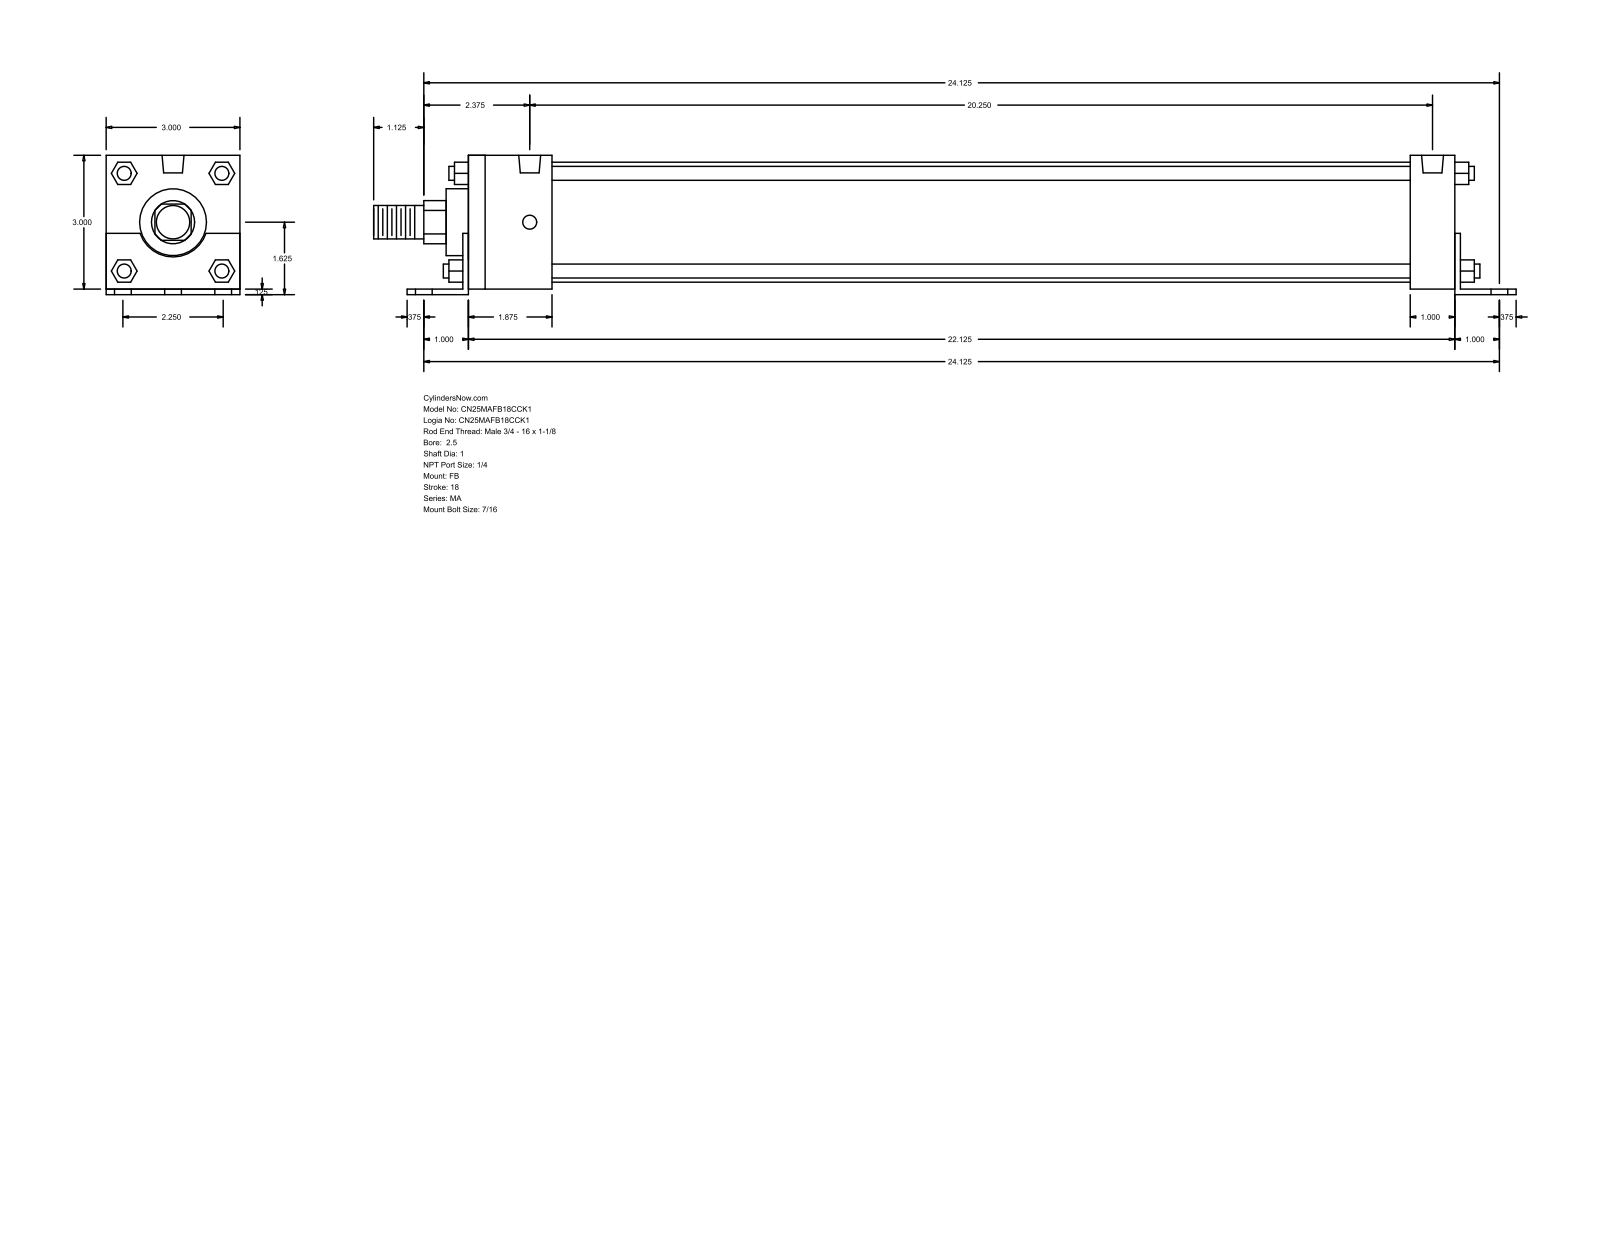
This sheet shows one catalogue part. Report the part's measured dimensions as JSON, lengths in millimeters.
{"part_name": "MA_FB__0250_1", "step_written_by": "GSSL Pune (CONFIG_CONTROL_DESIGN)", "units": "millimeters", "bodies": {"solids": 0, "faces": 140, "planar": 105, "cylindrical": 35, "other": 0}, "overall_size": [650.88, 79.38, 76.2], "round_holes": [[11.11, 6], [7.94, 4], [12.49, 2]], "round_bosses_or_shafts": [[7.94, 4], [68.33, 1], [38.1, 1], [25.4, 1], [19.05, 1]], "partial_cylinders_radius": [[12.29, 1], [19.81, 1]], "face_to_face_distances": [76.2, 3.17, 79.37, 565.15, 561.98, 12.7, 28.57, 25.4, 50.8, 47.63], "hole_center_spacings": [28.57, 613.44, 612.77, 47.62, 57.14, 66.75, 514.34, 553.18]}
